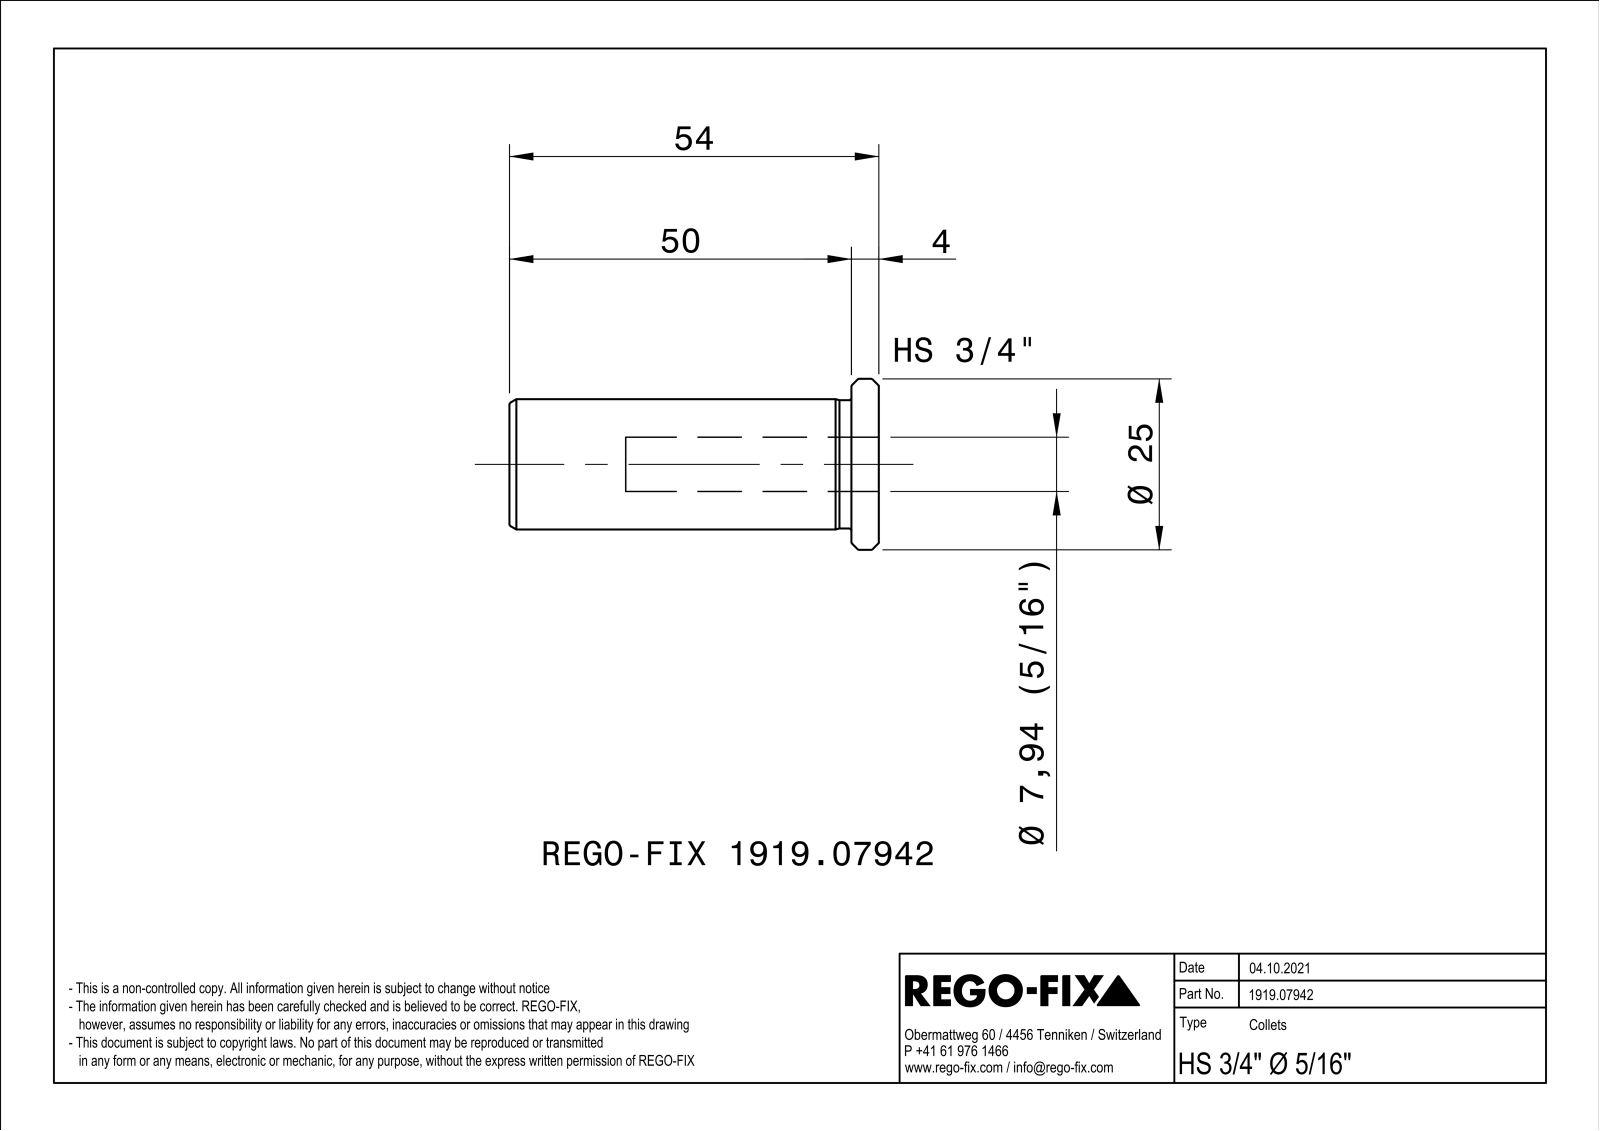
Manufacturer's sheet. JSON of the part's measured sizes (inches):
{"part_name": "NOCUT", "step_written_by": "SIEMENS PLM Software Solid Edge ST10 (AUTOMOTIVE_DESIGN)", "units": "inches", "bodies": {"solids": 1, "faces": 72, "planar": 22, "cylindrical": 12, "other": 38}, "overall_size": [2.126, 0.983, 0.983], "volume_in3": 0.64, "surface_area_in2": 11.09, "round_holes": [[0.313, 1], [0.413, 1], [0.65, 1]], "round_bosses_or_shafts": [[0.984, 1], [0.75, 1], [0.738, 1]], "face_to_face_distances": [0.039, 0.157, 2.126, 1.969]}
